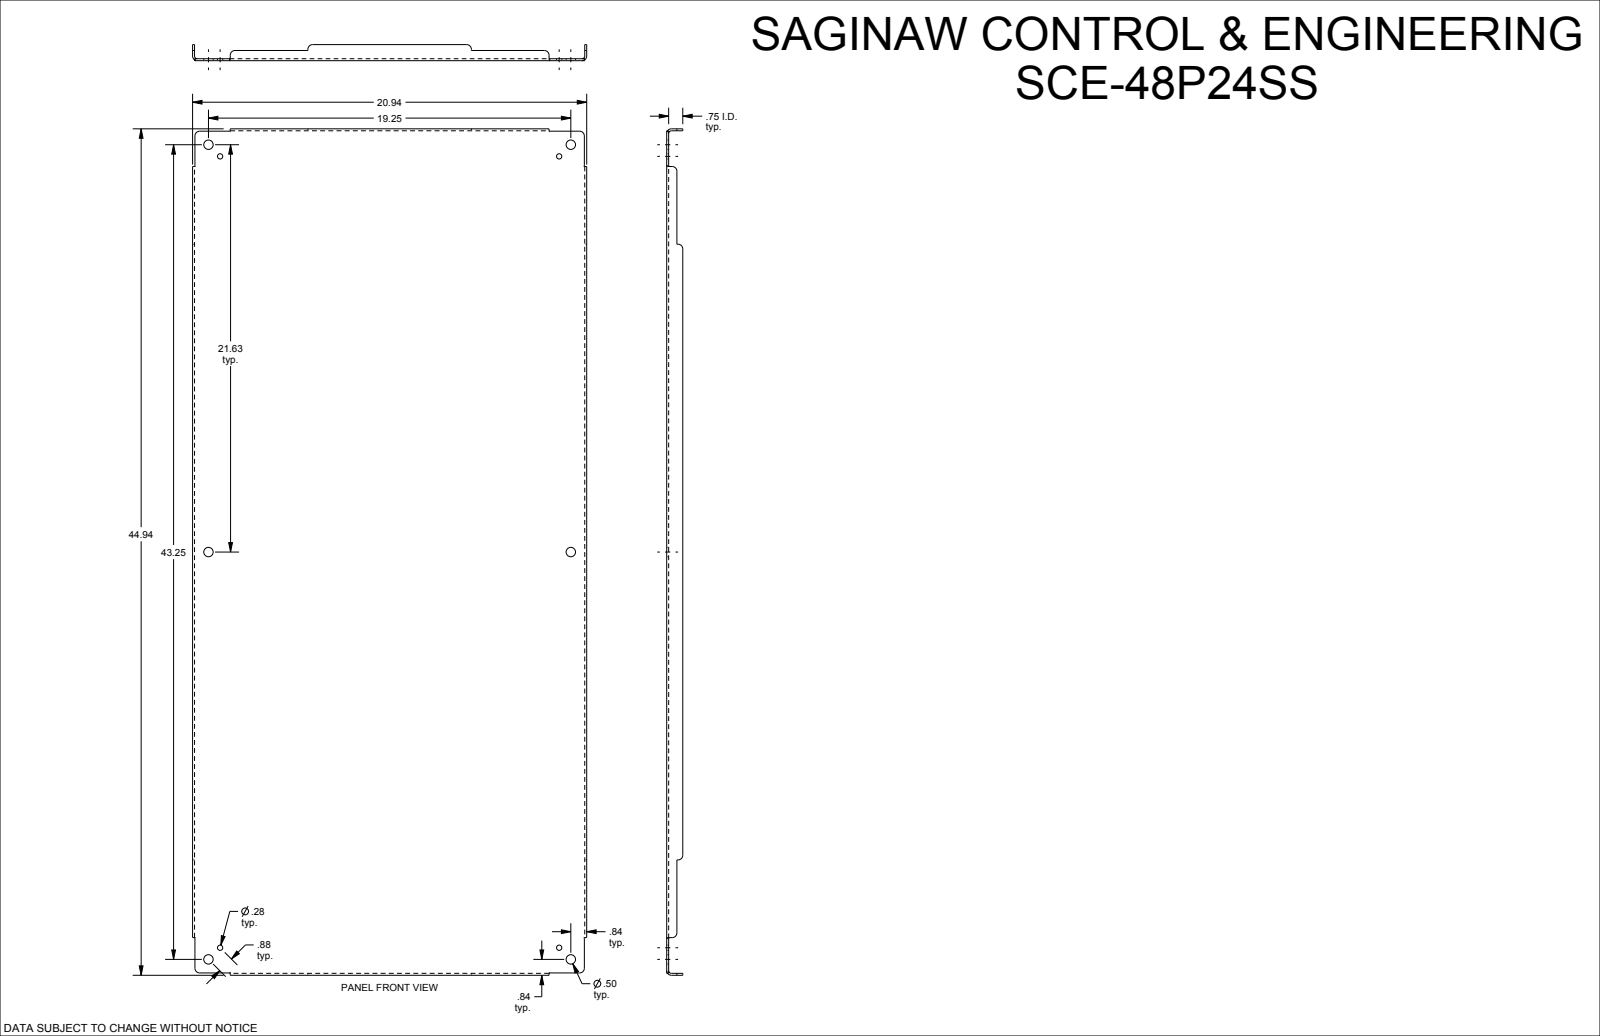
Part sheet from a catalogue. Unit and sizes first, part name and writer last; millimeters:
Units: millimetres
Overall size (bounding box): 1141.4 × 531.8 × 21.7
Round holes (diameter × count): ⌀12.7 ×6, ⌀7.1 ×4
Partial cylindrical surfaces — rounded edges, fillets, slot ends (radius × count): R6.4 ×12, R6.2 ×4, R3.6 ×2, R3.6 ×2
Main face-to-face distances: 2.6, 2.6, 529.2, 526.5, 531.8, 1138.8, 19.1, 21.7, 1141.4, 1136.1
Hole centre spacings: 22.2, 473.5, 533.8, 549.3, 713.2, 735.4, 1082.9, 1181.7
Volume: 1 711 000 mm³ · Surface area: 1 306 000 mm²
Bodies: 1 solid, 108 faces (46 planar, 38 cylindrical, 24 other)
Part name (STEP PRODUCT): SCE-48P24SS
STEP written by: SolidWorks 2019 (CONFIG_CONTROL_DESIGN)
